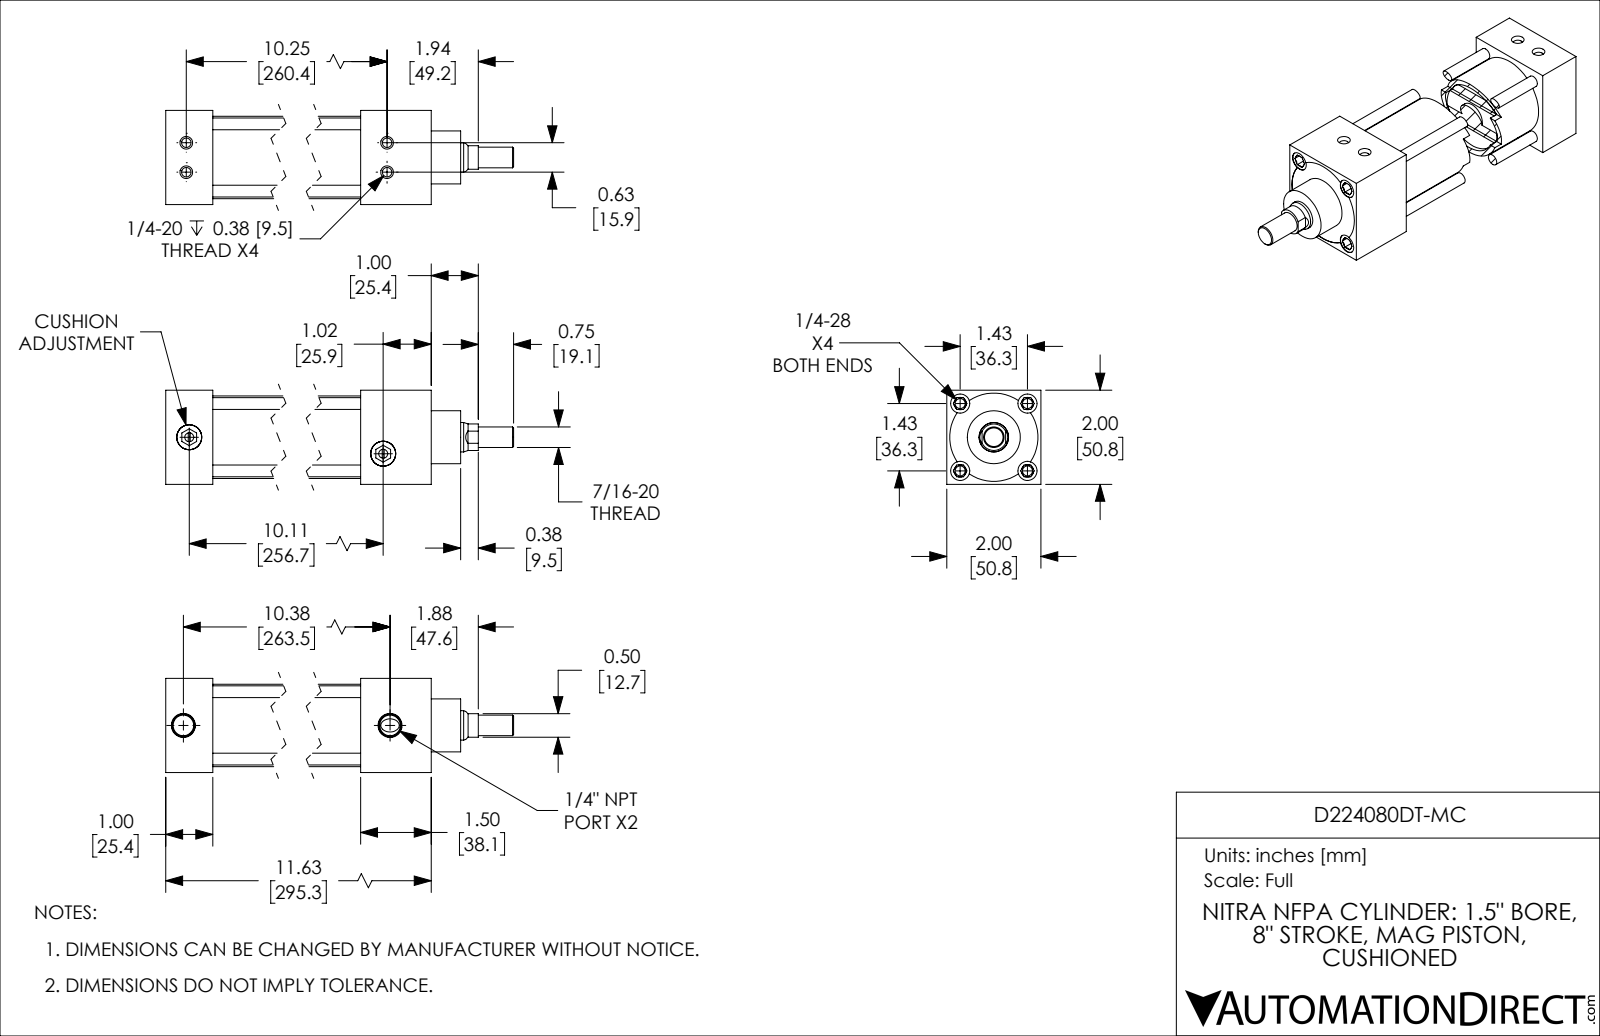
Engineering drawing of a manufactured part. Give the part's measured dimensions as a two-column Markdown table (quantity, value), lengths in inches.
| quantity | value |
| --- | --- |
| part name | D224080DT-MC_BODY; D224080DT-MC; D224080DT-MC_PISTON_KK1; D224080DT-MC_CUSHION |
| STEP written by | SolidWorks 2019 (CONFIG_CONTROL_DESIGN) |
| units | inches |
| bodies | 4 solids, 251 faces (90 planar, 81 cylindrical, 80 other) |
| overall size | 13.375 × 2 × 2 |
| volume | 22.3 in³ |
| surface area | 201.4 in² |
| round holes (diameter × count) | 0.201 × 4, 0.213 × 4, 0.406 × 4, 0.19 × 2, 0.438 × 2, 0.531 × 2, 0.626 × 1, 1.501 × 1 |
| round bosses / shafts (diameter × count) | 0.25 × 4, 0.532 × 2, 1.751 × 1, 1.499 × 1, 1.125 × 1, 0.624 × 1, 0.437 × 1 |
| partial cylindrical surfaces (radius × count) | 0.281 × 1, 0.937 × 1 |
| main face-to-face distances | 2, 1, 10.125, 9.125, 2.125, 11.62, 10.62, 1.495, 1.125, 8 |
| hole center spacings | 0.319, 1.011, 1.43, 0.625, 2.022, 10.25, 10.269, 10.317 |
